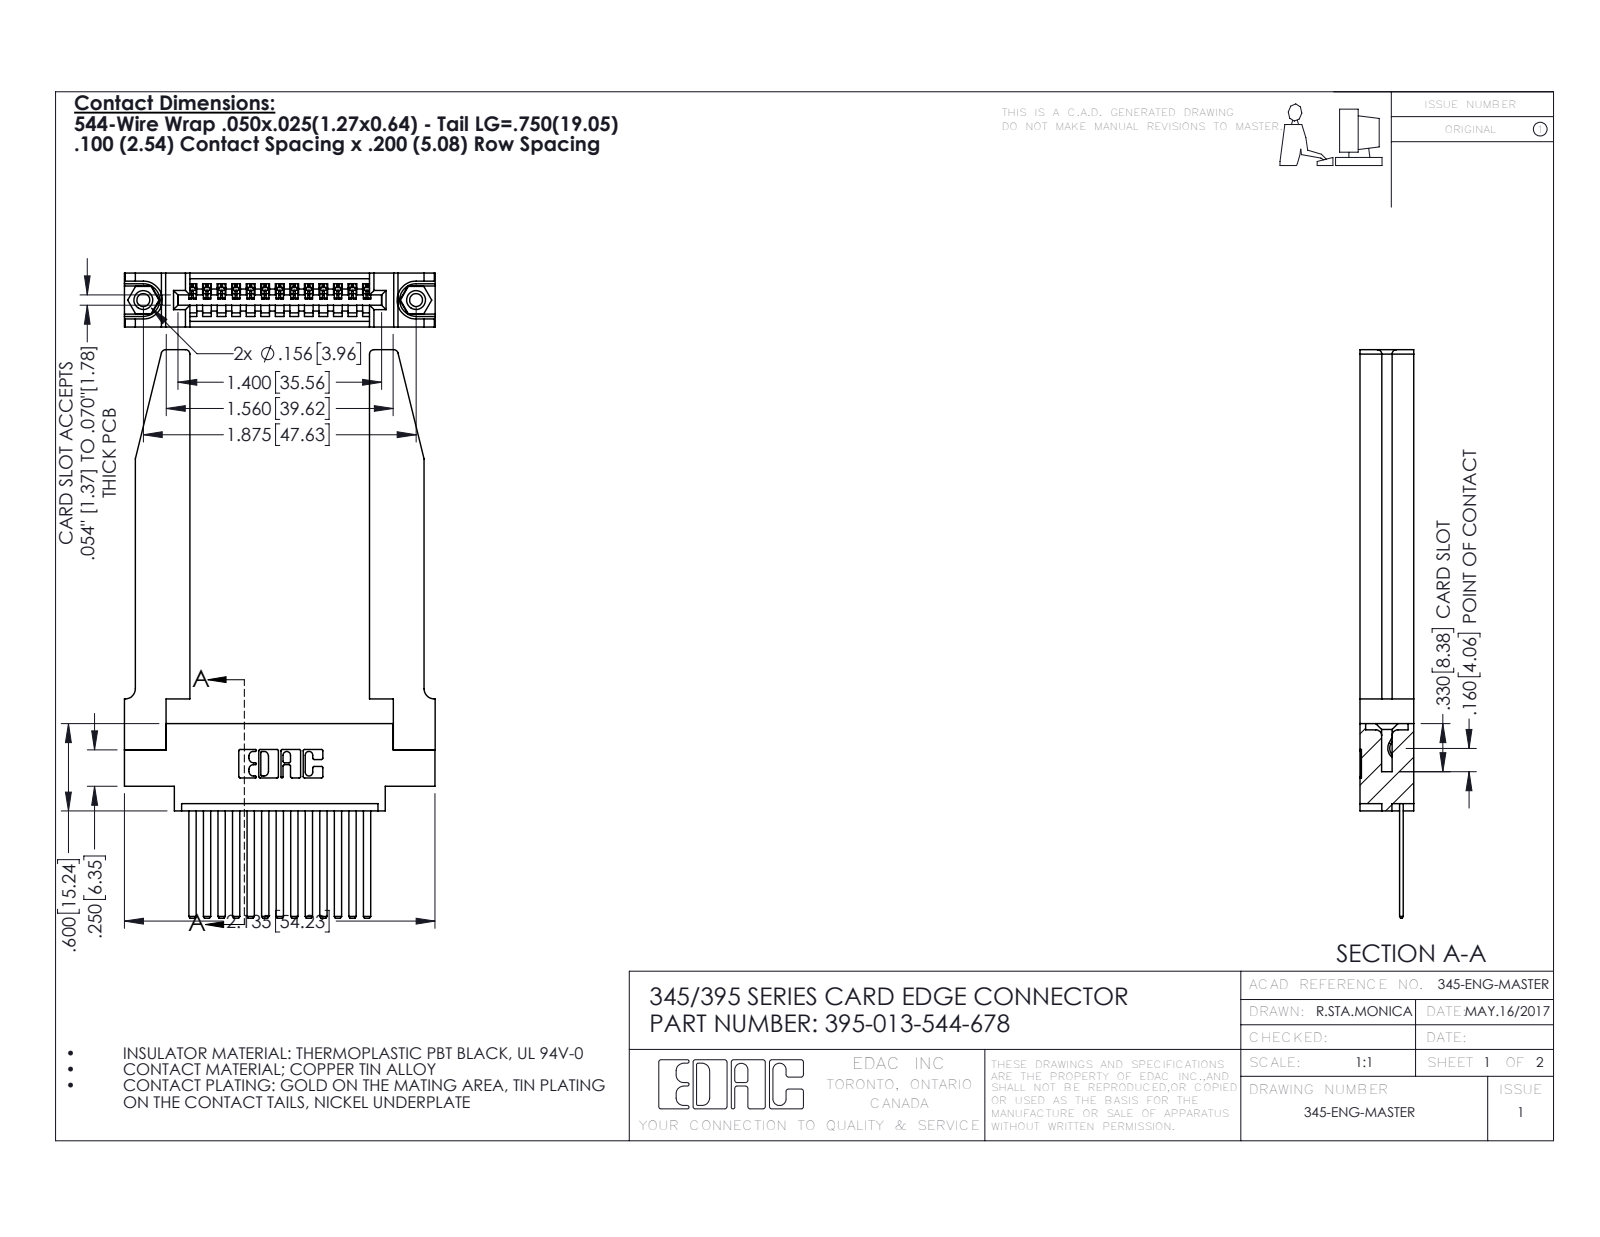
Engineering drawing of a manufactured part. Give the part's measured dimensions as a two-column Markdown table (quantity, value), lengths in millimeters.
| quantity | value |
| --- | --- |
| part name | 345-250-001_345-250-001-102; 345-292-001_345-293-144; 395-013-544-678; 345-220-078_345-220-078 (+1 more) |
| STEP written by | SolidWorks 2016 (CONFIG_CONTROL_DESIGN) |
| units | millimeters |
| bodies | 18 solids, 1040 faces (694 planar, 294 cylindrical, 52 other) |
| overall size | 99.2 × 54.3 × 9.4 |
| volume | 12 700 mm³ |
| surface area | 13 610 mm² |
| round holes (diameter × count) | 2.3 × 2, 3.2 × 2, 4 × 2, 1.6 × 1 |
| round bosses / shafts (diameter × count) | 3.9 × 2 |
| partial cylindrical surfaces (radius × count) | 0.2 × 26, 0.3 × 22, 0.8 × 8, 0.2 × 6, 0.8 × 6, 0.7 × 3, 0.8 × 2, 1 × 2 |
| main face-to-face distances | 9.4, 1.8, 7.6, 2.5, 6.9, 0.6, 3.8, 3.8, 5.6, 2 |
| hole center spacings | 6.9, 41.7, 47.6 |
